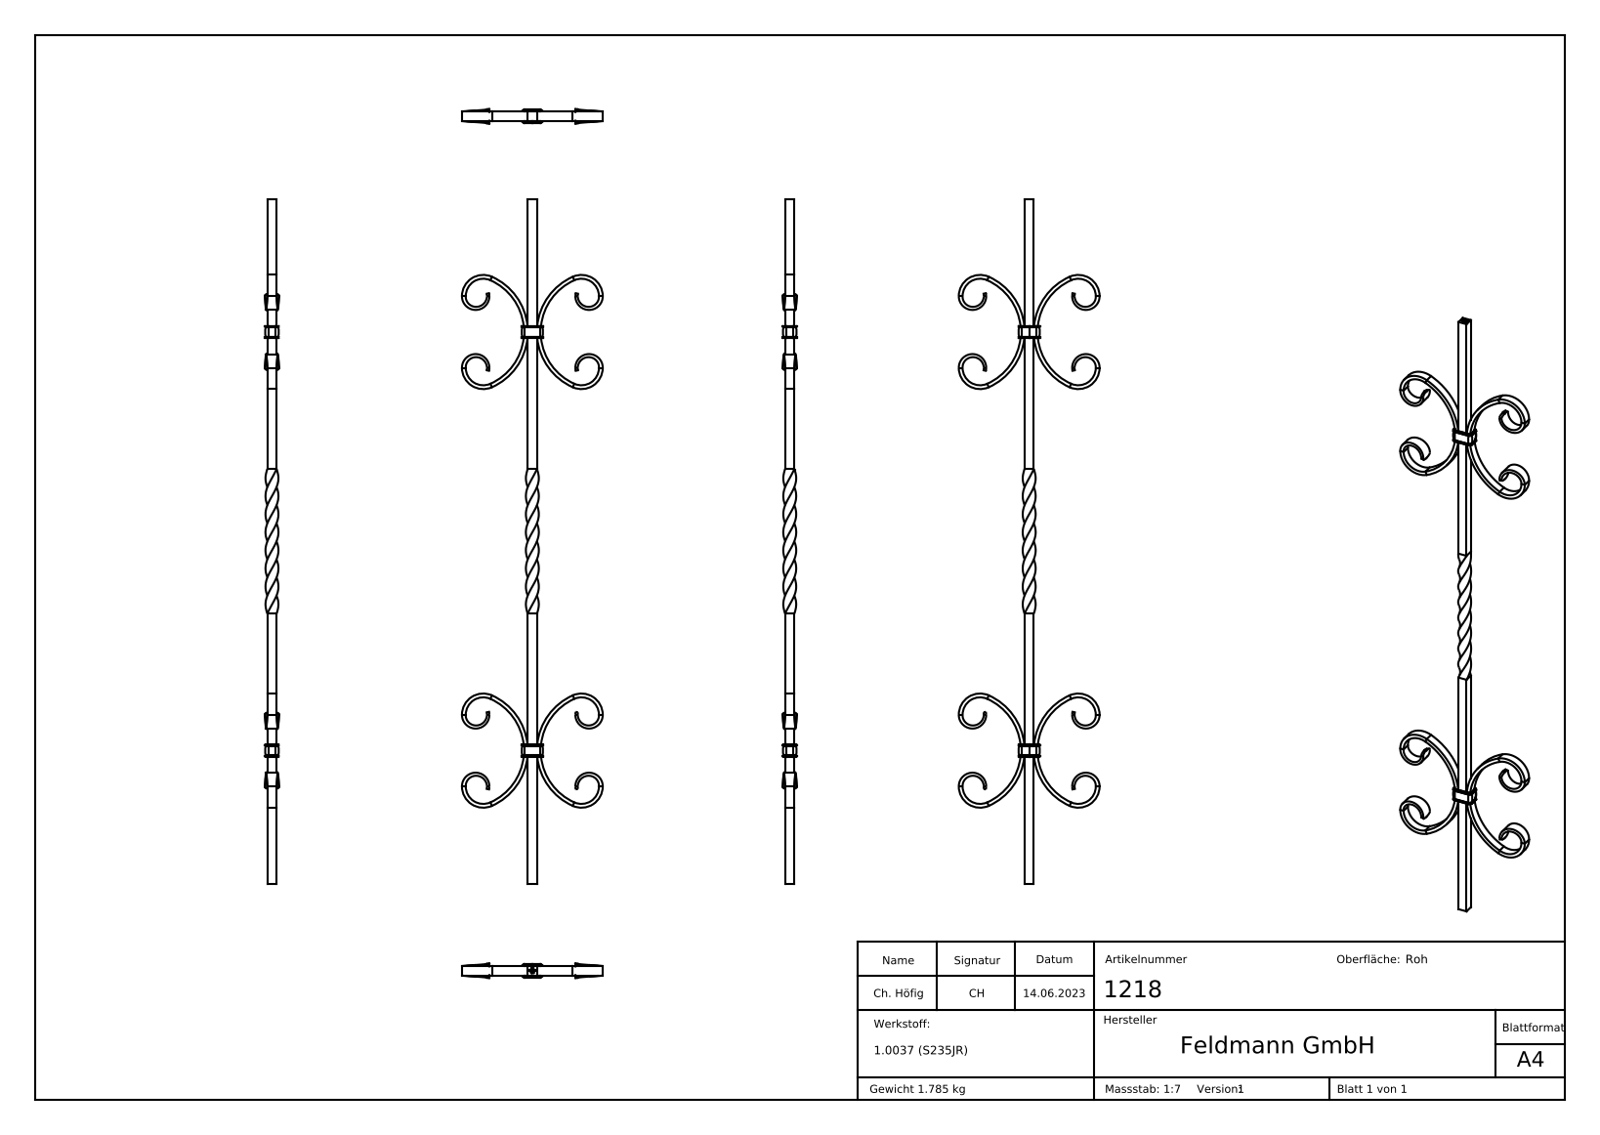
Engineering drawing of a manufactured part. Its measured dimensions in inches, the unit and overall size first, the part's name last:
Units: inches
Overall size (bounding box): 35.433 × 7.283 × 0.732
Partial cylindrical surfaces — rounded edges, fillets, slot ends (radius × count): R0.02 ×48, R0.008 ×16, R0.851 ×8, R0.906 ×8, R1.102 ×8, R0.039 ×4, R0.157 ×4, R2.931 ×4
Main face-to-face distances: 0.472, 0.197, 0.669, 21.654, 0.63, 0.866, 6.575, 7.205, 28.228, 28.858
Volume: 13.96 in³ · Surface area: 160.7 in²
Bodies: 6 solids, 612 faces (259 planar, 138 cylindrical, 215 other)
Part name (STEP PRODUCT): 1218
STEP written by: SolidWorks 2018 (CONFIG_CONTROL_DESIGN)
